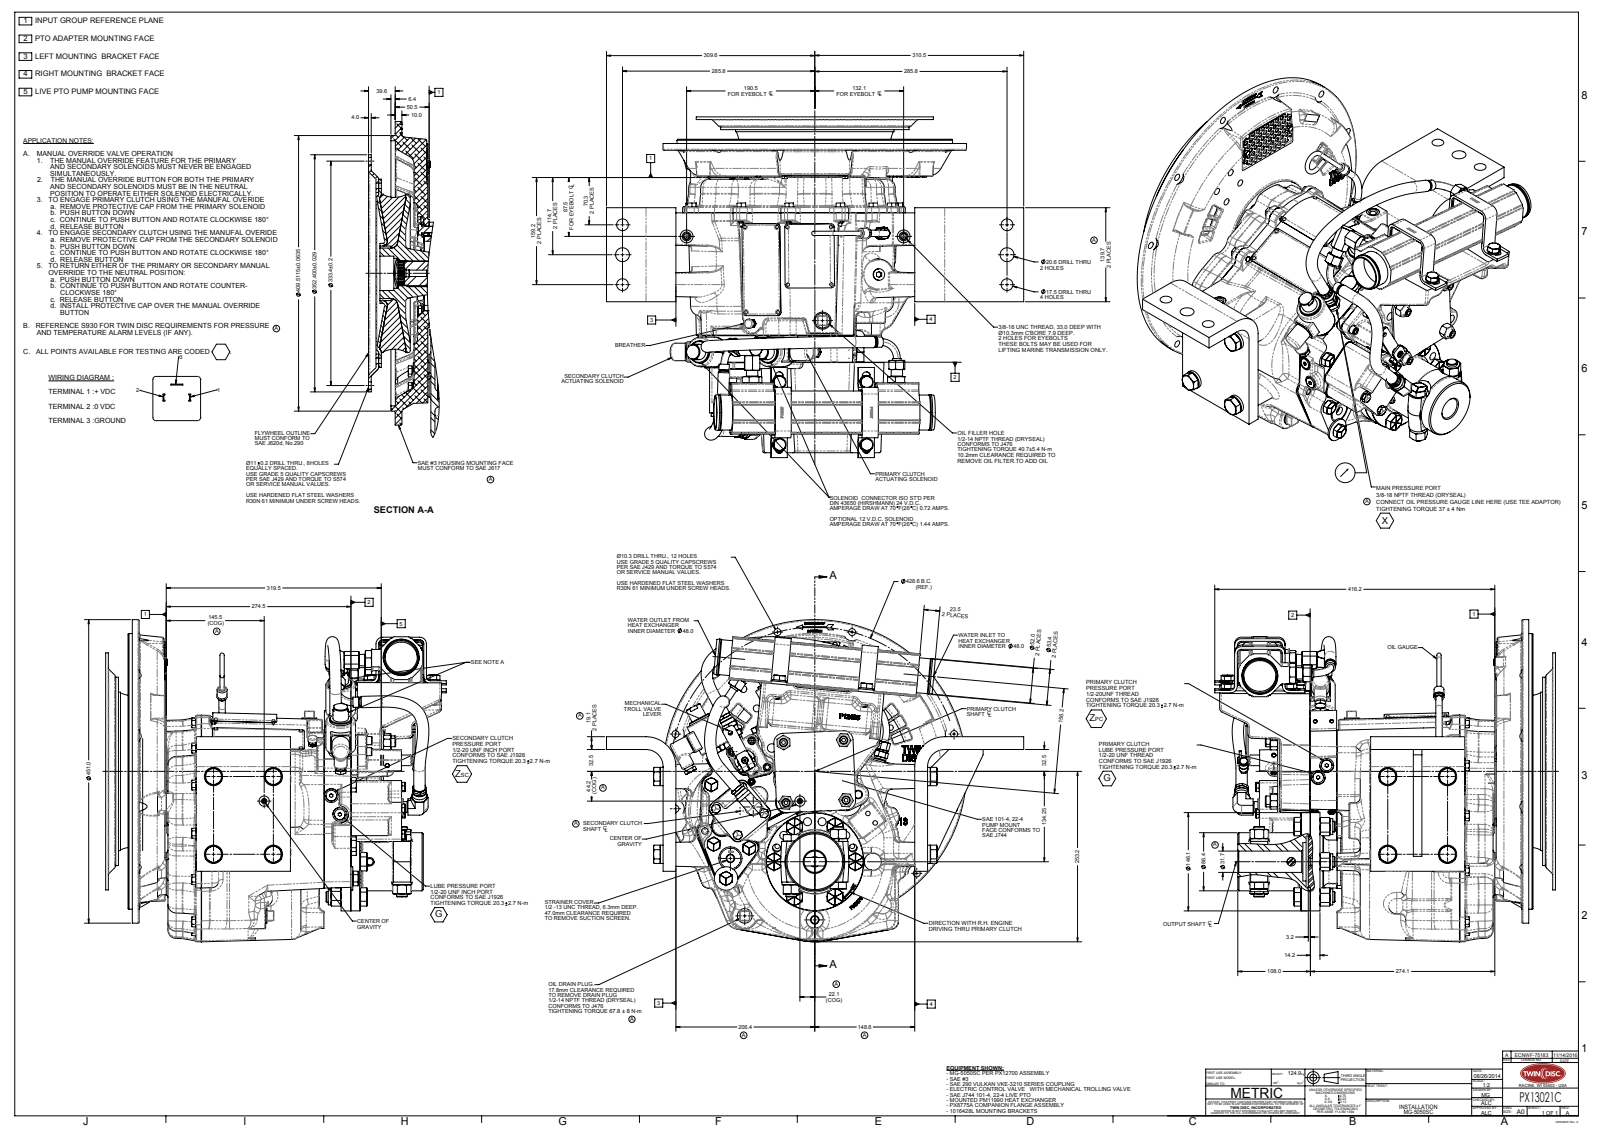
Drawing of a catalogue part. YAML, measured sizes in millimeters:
part_name: "PX13021C"
step_written_by: "SolidWorks 2010 (AUTOMOTIVE_DESIGN)"
units: millimeters
bodies: {solids: 0, faces: 4560, planar: 1282, cylindrical: 1307, other: 1971}
overall_size: [620.1, 506.28, 478.74]
round_holes:
  - {diameter: 7, count: 50}
  - {diameter: 10.32, count: 13}
  - {diameter: 8.2, count: 12}
  - {diameter: 11, count: 8}
  - {diameter: 11.91, count: 6}
  - {diameter: 20.64, count: 6}
  - {diameter: 10.3, count: 4}
  - {diameter: 12.7, count: 4}
  - {diameter: 17.46, count: 4}
  - {diameter: 7.14, count: 3}
  - {diameter: 7.94, count: 3}
  - {diameter: 5.33, count: 2}
round_bosses_or_shafts:
  - {diameter: 23.62, count: 9}
  - {diameter: 27.23, count: 6}
  - {diameter: 15.77, count: 6}
  - {diameter: 23.71, count: 5}
  - {diameter: 19, count: 4}
  - {diameter: 16.9, count: 4}
  - {diameter: 15.87, count: 4}
  - {diameter: 12.56, count: 4}
partial_cylinders:
  - {radius: 1.5, count: 90}
  - {radius: 8.13, count: 54}
  - {radius: 1.52, count: 51}
  - {radius: 2.5, count: 49}
  - {radius: 0.4, count: 32}
  - {radius: 6.5, count: 30}
  - {radius: 8, count: 28}
  - {radius: 13, count: 24}
face_to_face_distances: [19.05, 4, 236.3, 374.04, 0.79, 237.09, 4.54, 232.55, 231.76, 15]
hole_center_spacings: [214.3, 214.31, 371.19, 10, 110.93, 303.07, 414.01, 20]
